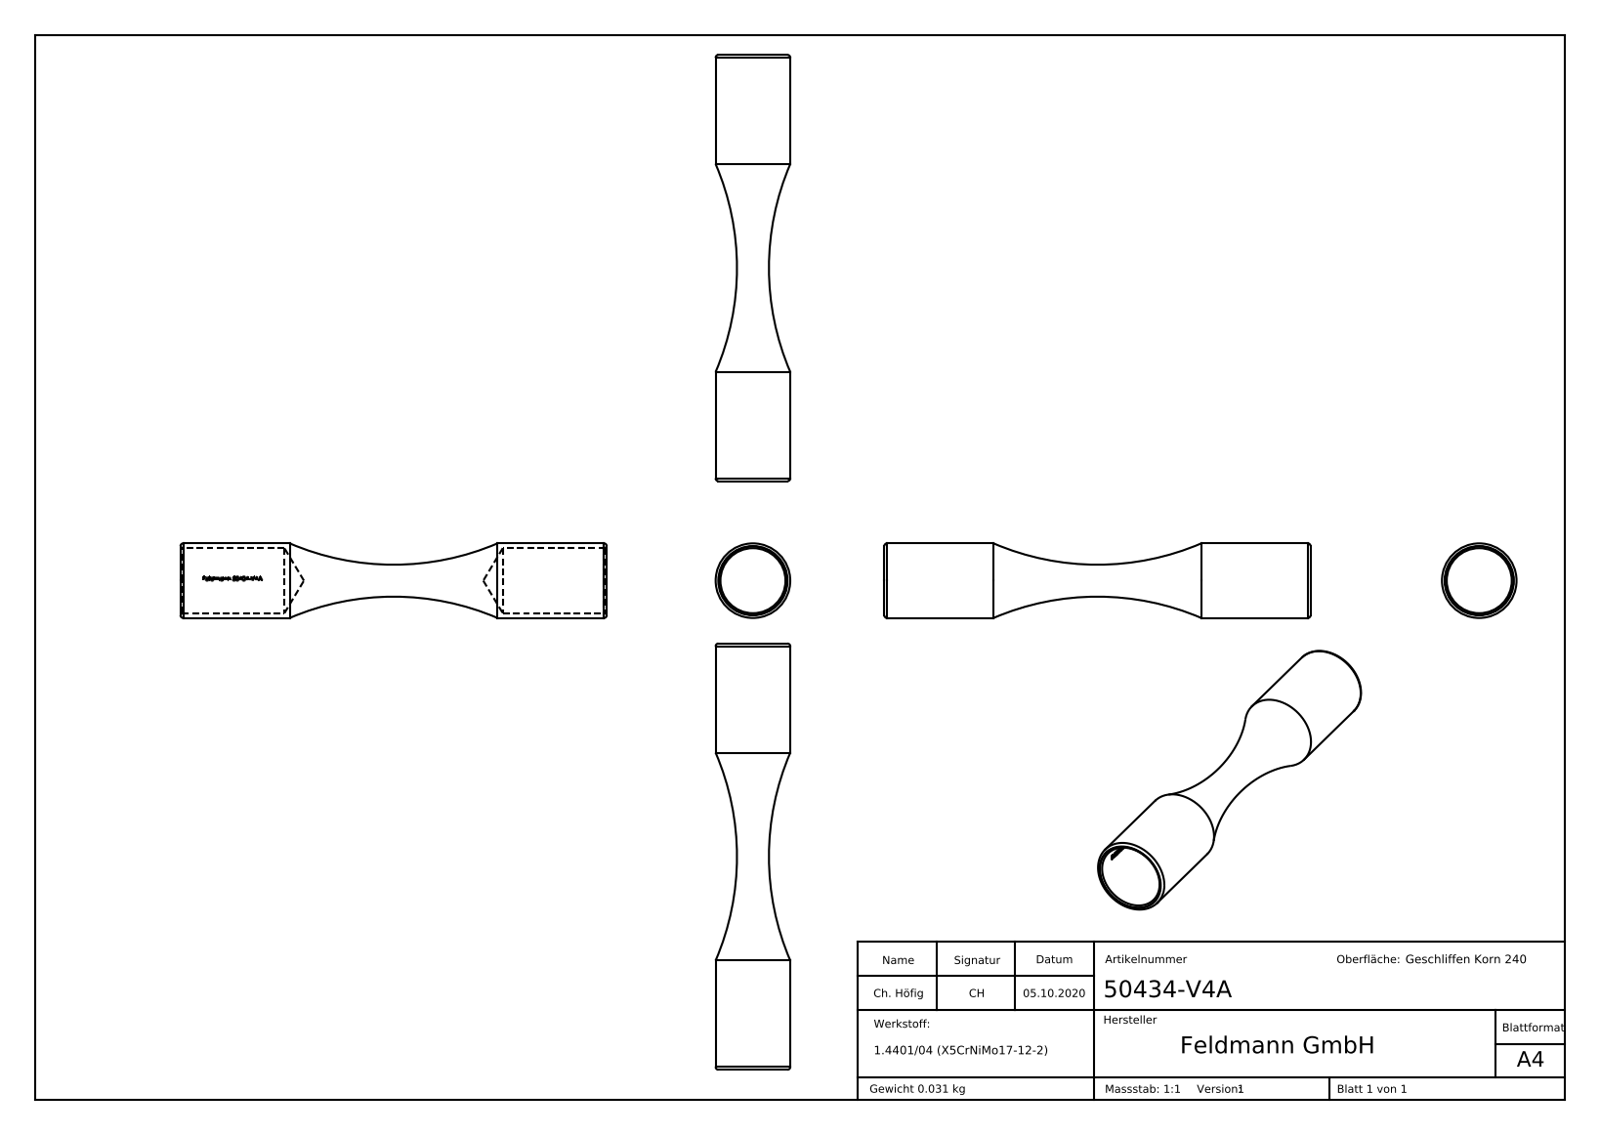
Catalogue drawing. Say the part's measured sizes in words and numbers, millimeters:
The part is named "50434-V4A". Its 3-D file was written by "SolidWorks 2018 (CONFIG_CONTROL_DESIGN)". It is 1 solid with 267 faces: 126 planar, 46 cylindrical and 95 other. Overall it measures 79.99 by 14 by 14 millimeters. Its volume is 3 907 cubic millimeters and its surface area 4 711 square millimeters. Round holes: 1 of diameter 12.2. Round bosses or shafts: 1 of diameter 14. Partial cylindrical surfaces (rounded edges, fillets, slot ends): 1 of radius 6.2. The main face-to-face distances are 79.98, 5.49, 8.93, 4.65, 0.53, 1.21, 3.75, 0.83, 0.44, 1.74.
